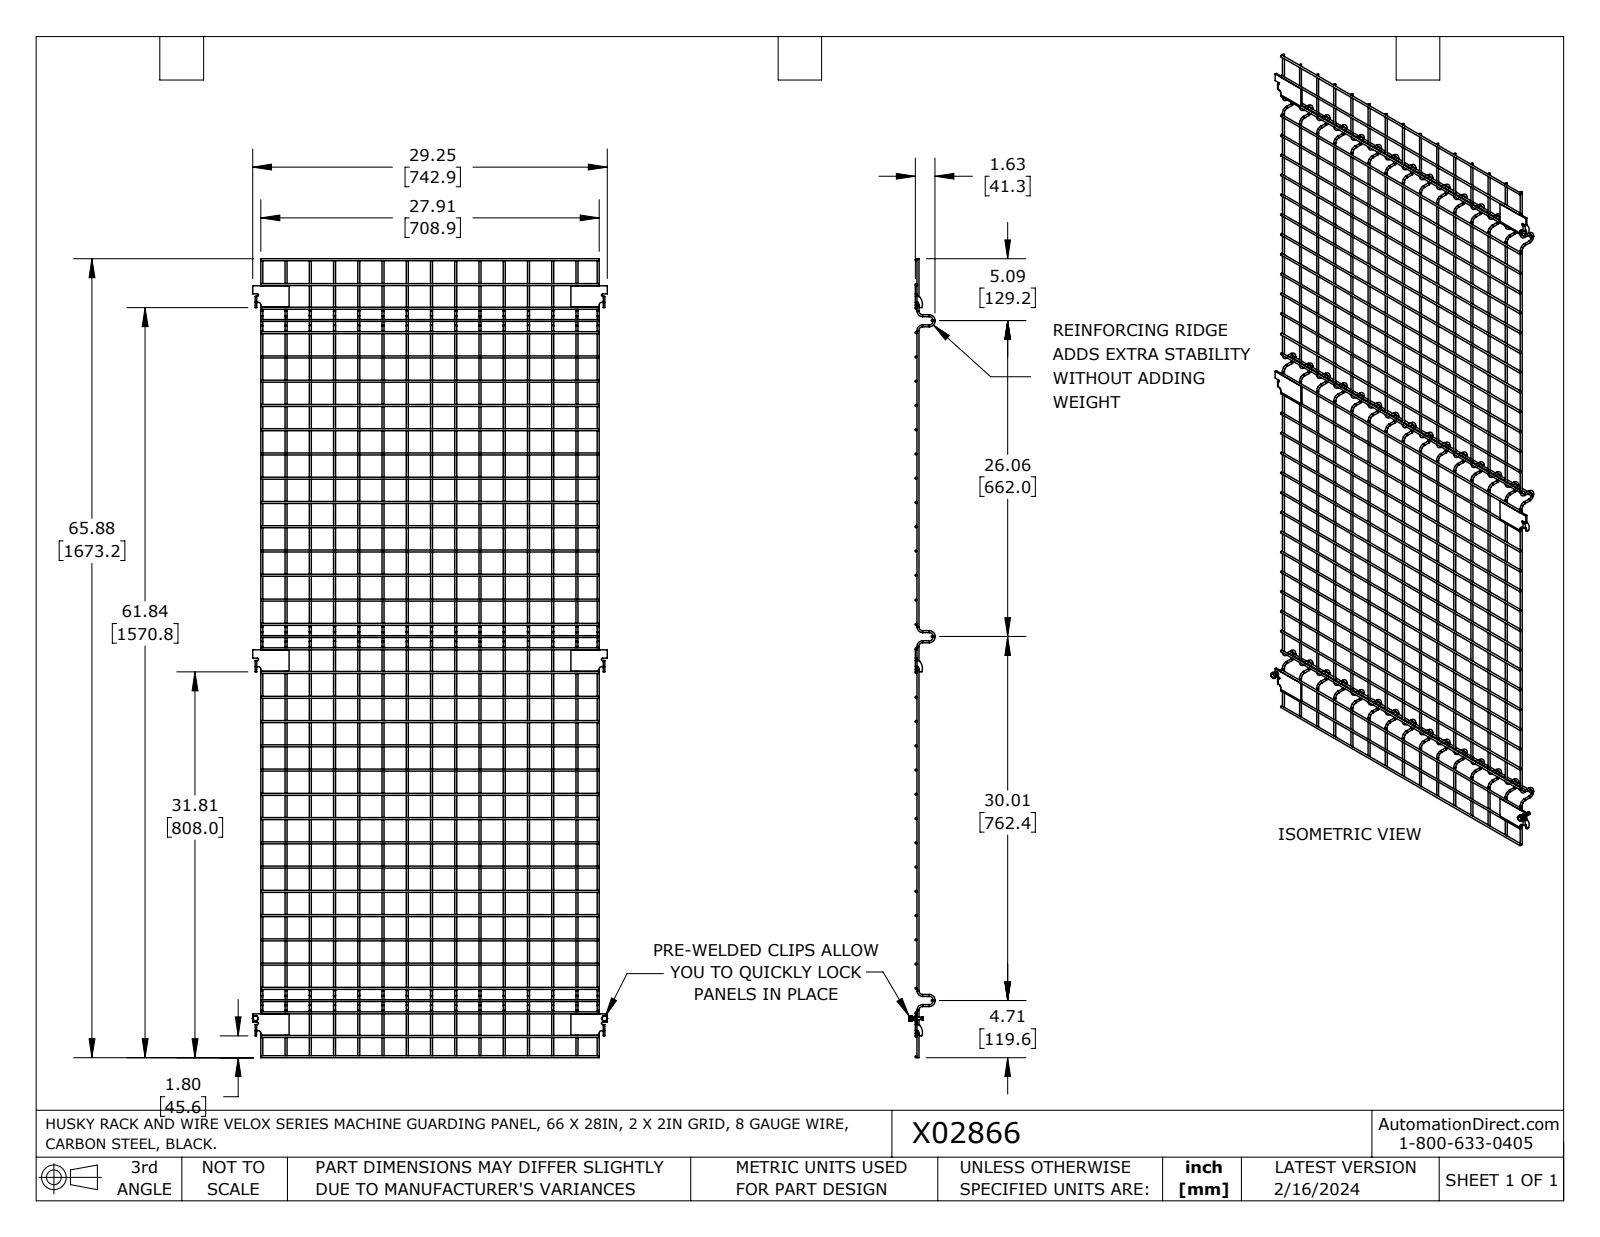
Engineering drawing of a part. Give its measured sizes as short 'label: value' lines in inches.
name: X02866
written by: SolidWorks 2023 (AUTOMOTIVE_DESIGN)
unit: in
bodies: 62 solids, 696 faces (212 planar, 280 cylindrical, 204 other)
size: 65.875 × 29.313 × 2.103
volume: 46.57 in³; area: 1 137 in²
holes: 2× ⌀0.201, 2× ⌀0.25
bosses: 157× ⌀0.16, 2× ⌀0.39, 2× ⌀0.245, 2× ⌀0.187
rounds: 6× R0.1, 6× R0.218, 3× R0.25, 3× R0.865, 2× R0.009, 2× R0.067, 2× R0.134
face distances: 0.134, 0.125, 1.765, 30.031, 0.467, 28.377, 30.016, 60.047, 2.798, 26.046
hole spacings: 28.808
